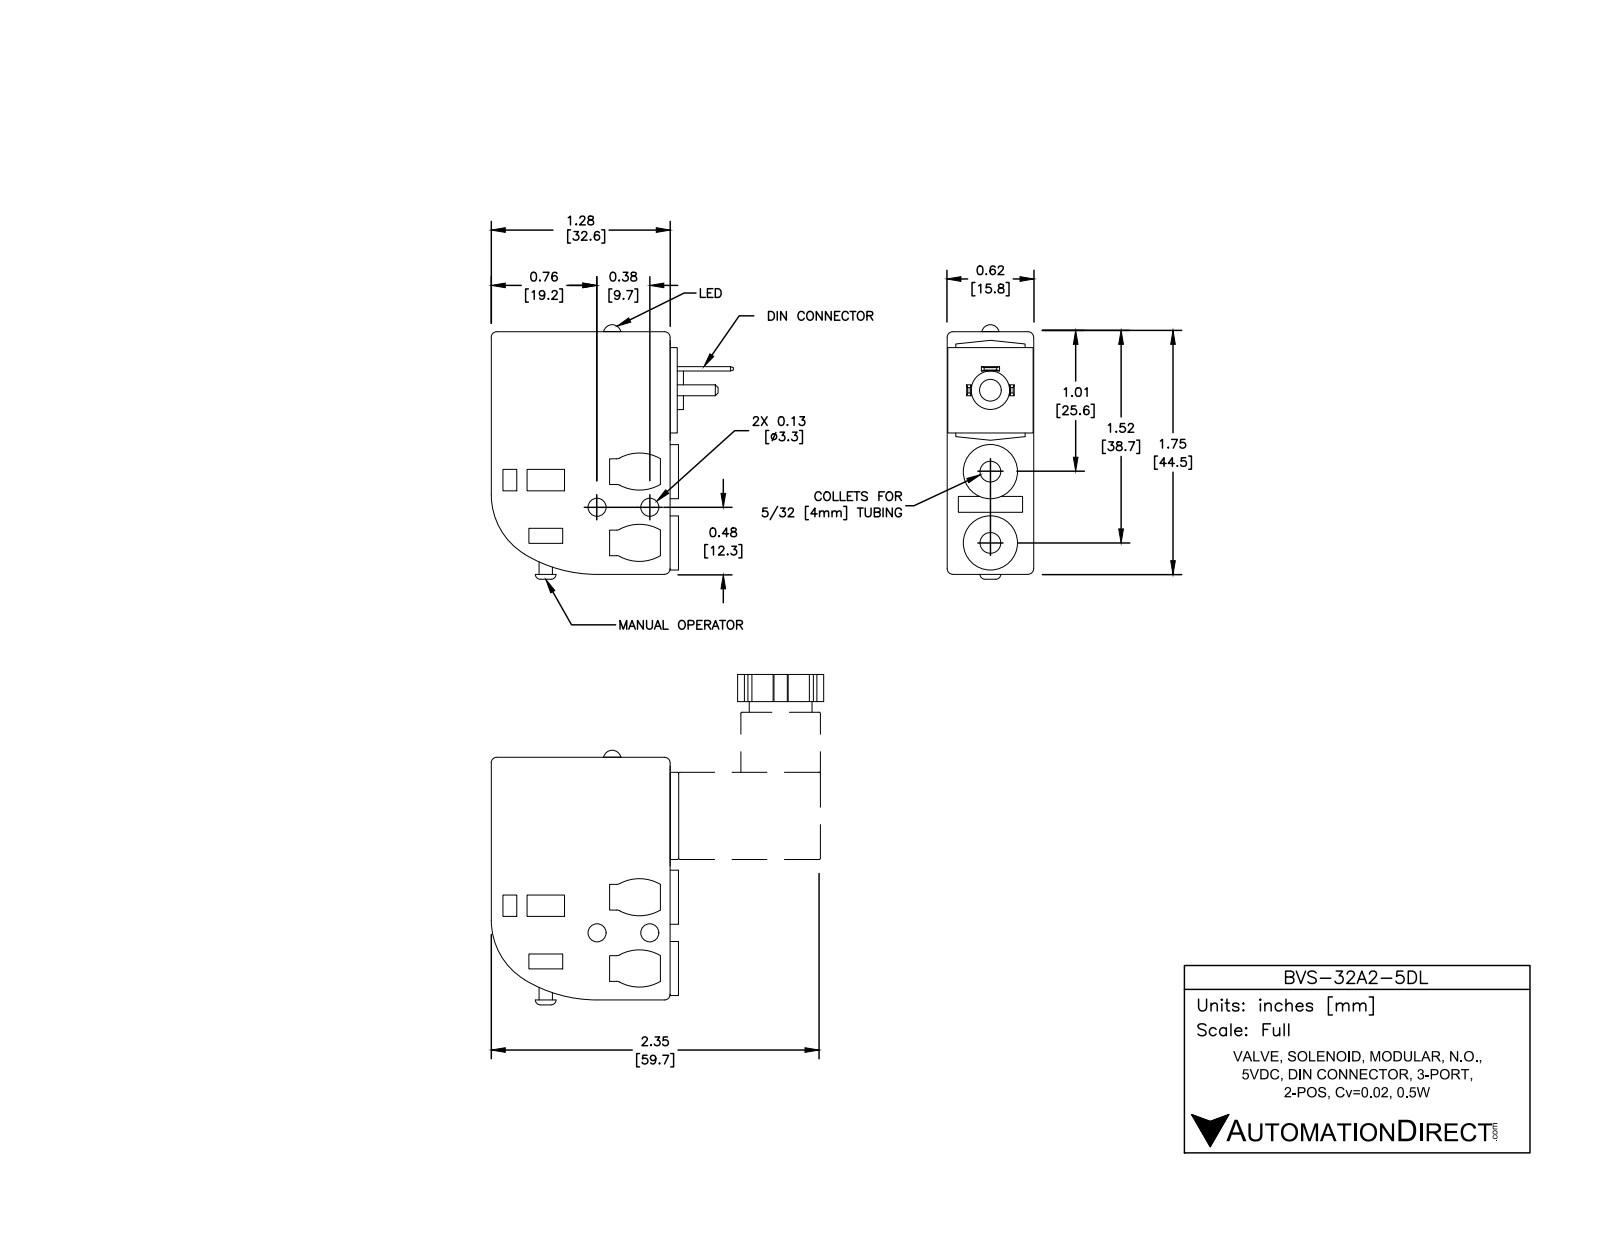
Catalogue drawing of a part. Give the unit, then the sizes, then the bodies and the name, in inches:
Units: inches
Overall size (bounding box): 1.84 × 1.75 × 0.62
Round holes (diameter × count): ⌀0.13 ×2, ⌀0.15 ×2, ⌀0.25 ×2, ⌀0.05 ×1, ⌀0.16 ×1
Round bosses / shafts (diameter × count): ⌀0.39 ×2, ⌀0.28 ×1, ⌀0.1 ×1
Partial cylindrical surfaces — rounded edges, fillets, slot ends (radius × count): R0.05 ×4, R0.3 ×4, R0.04 ×3, R0.5 ×1, R1 ×1
Main face-to-face distances: 0.62, 0.1, 1.29, 0.52, 1.341, 0.051, 1.75, 1, 0.15, 0.06
Hole centre spacings: 0.06, 0.38, 0.45, 0.51, 0.59, 0.65, 1.1
Volume: 1.279 in³ · Surface area: 10.75 in²
Bodies: 1 solid, 162 faces (112 planar, 46 cylindrical, 4 other)
Part name (STEP PRODUCT): BVS-32A2-5DL
STEP written by: SolidWorks 2016 (AUTOMOTIVE_DESIGN)
